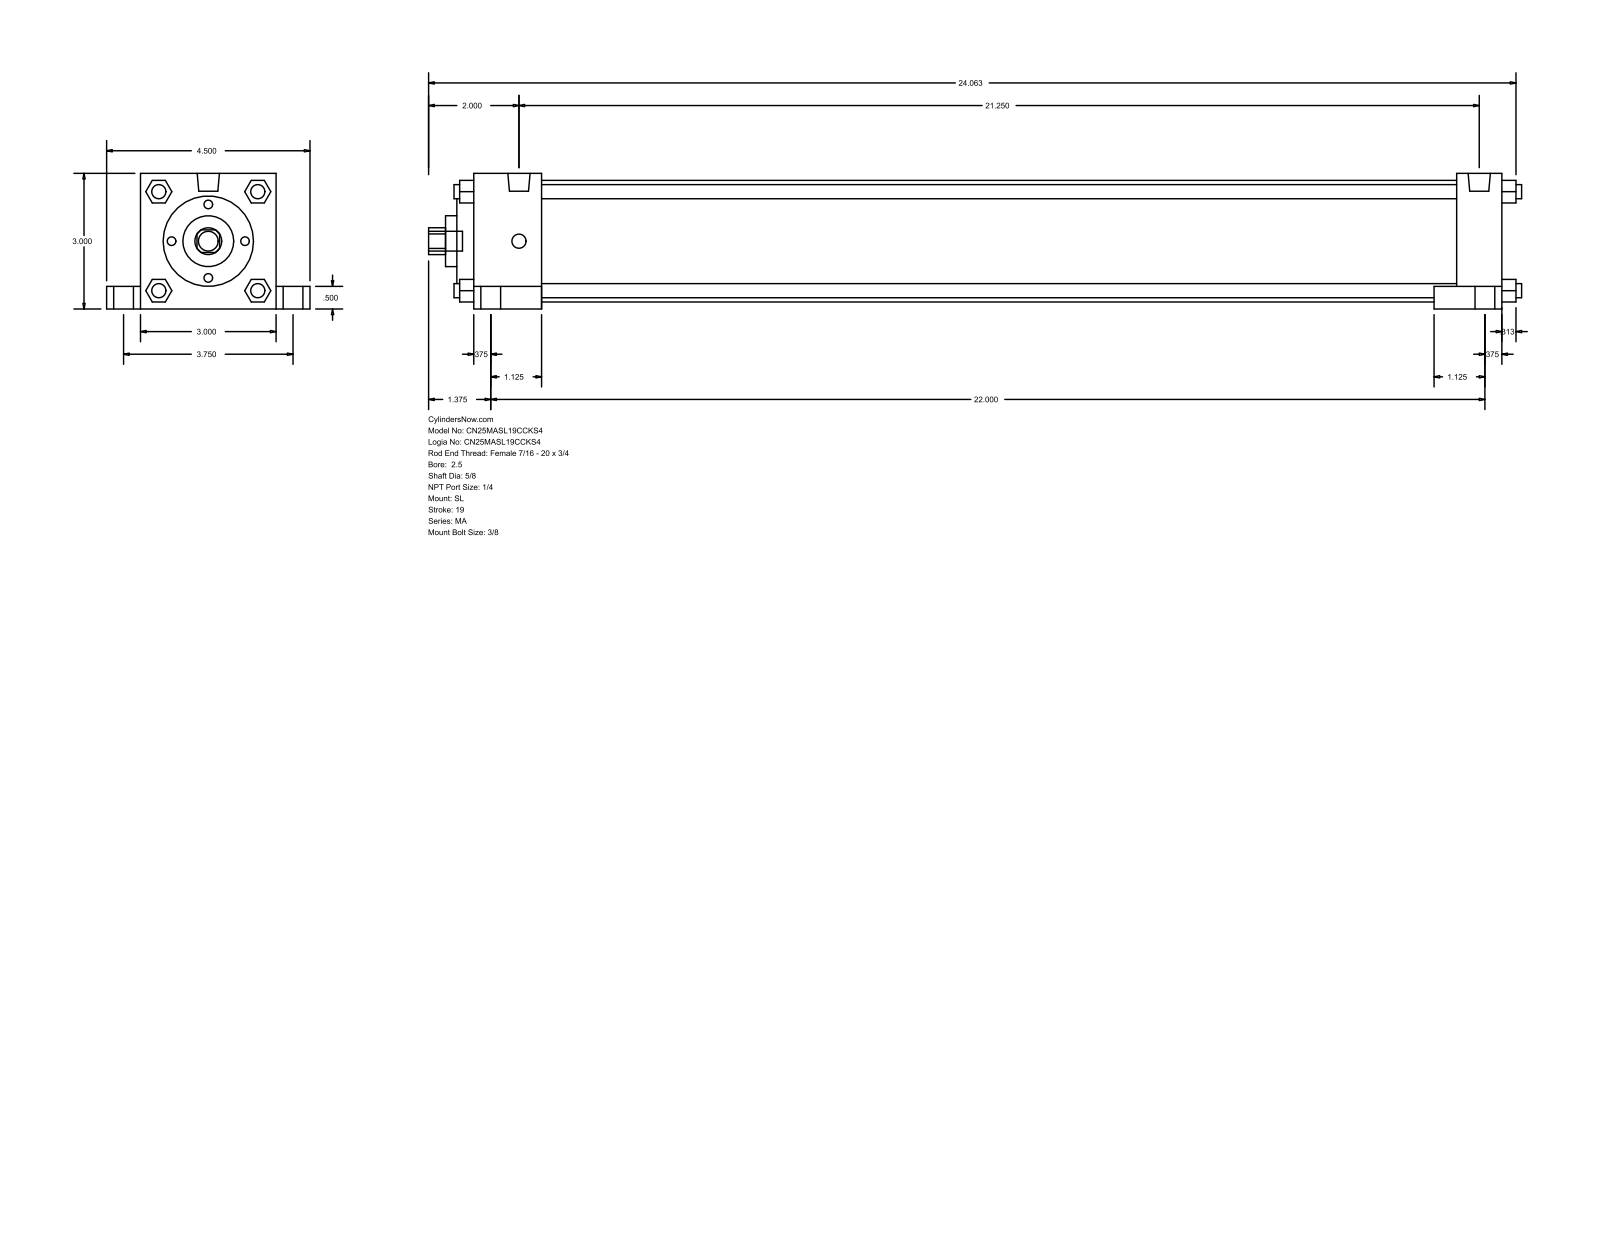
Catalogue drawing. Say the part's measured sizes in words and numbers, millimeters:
The part is named "MA_SL__0250_0.625". Its 3-D file was written by "GSSL Pune (CONFIG_CONTROL_DESIGN)". It is 0 solids with 150 faces: 113 planar, 37 cylindrical and 0 other. Overall it measures 614.36 by 114.3 by 76.2 millimeters. Round holes: 1 of diameter 15.88, 1 of diameter 28.57, 1 of diameter 50.8, 1 of diameter 68.33. Round bosses or shafts: 8 of diameter 7.94, 5 of diameter 11.11, 4 of diameter 17.46, 2 of diameter 12.49. Partial cylindrical surfaces (rounded edges, fillets, slot ends): 1 of radius 7.54. The main face-to-face distances are 76.2, 577.85, 12.7, 514.35, 25.4, 38.1, 539.75, 552.45, 19.05, 63.5.
